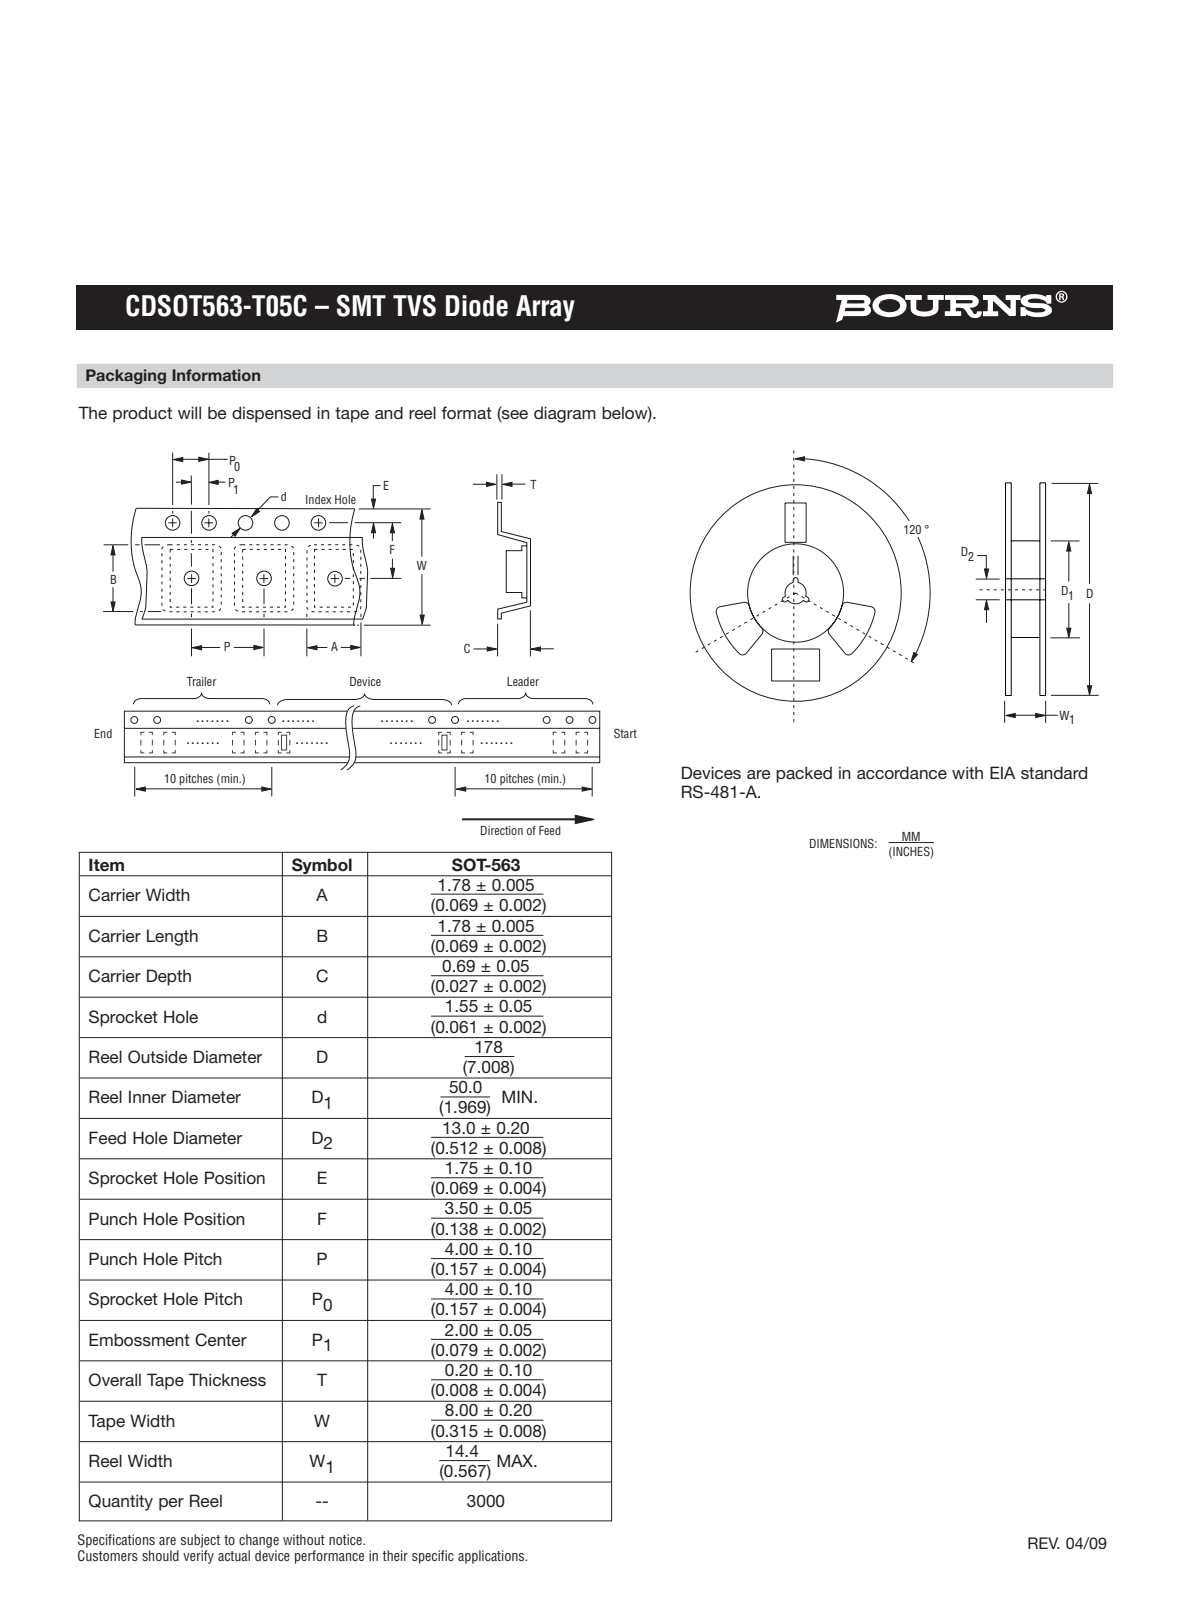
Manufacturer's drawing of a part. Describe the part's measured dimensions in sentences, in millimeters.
The part is named "CDSOT563-0502". Its 3-D file was written by "PRO/ENGINEER BY PARAMETRIC TECHNOLOGY CORPORATION, 2010100 (CONFIG_CONTROL_DESIGN)". It is 1 solid with 34 faces: 34 planar, 0 cylindrical and 0 other. Overall it measures 1.6 by 1.6 by 0.55 millimeters. Its volume is 1 cubic millimeters and its surface area 8 square millimeters. The main face-to-face distances are 0.55, 1.6, 0.43, 0.5, 1.4, 1.2, 0.41, 0.69, 0.91, 1.19.
